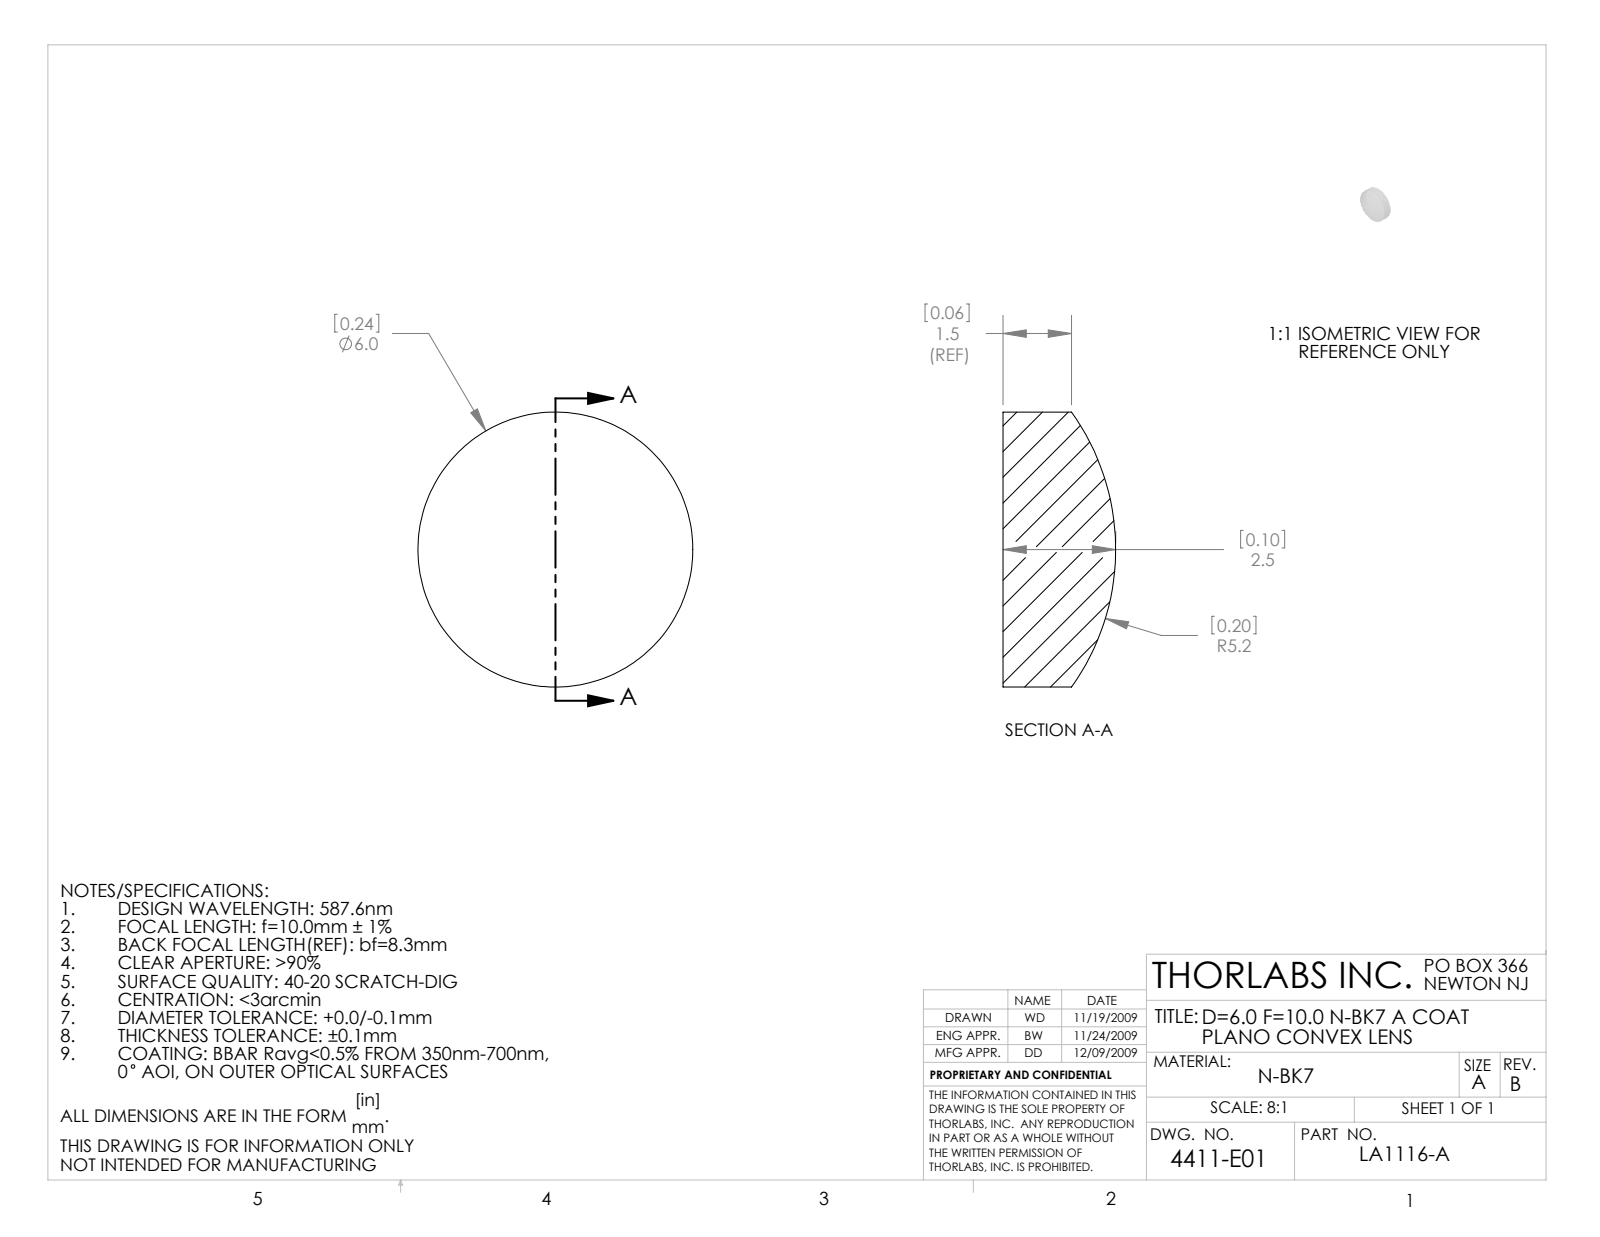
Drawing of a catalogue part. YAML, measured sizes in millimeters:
part_name: "4411-E0W"
step_written_by: "SolidWorks 2009 (AUTOMOTIVE_DESIGN)"
units: millimeters
bodies: {solids: 1, faces: 5, planar: 1, cylindrical: 2, other: 2}
overall_size: [6, 6, 2.46]
volume: 56
surface_area: 88
round_bosses_or_shafts:
  - {diameter: 6, count: 1}
